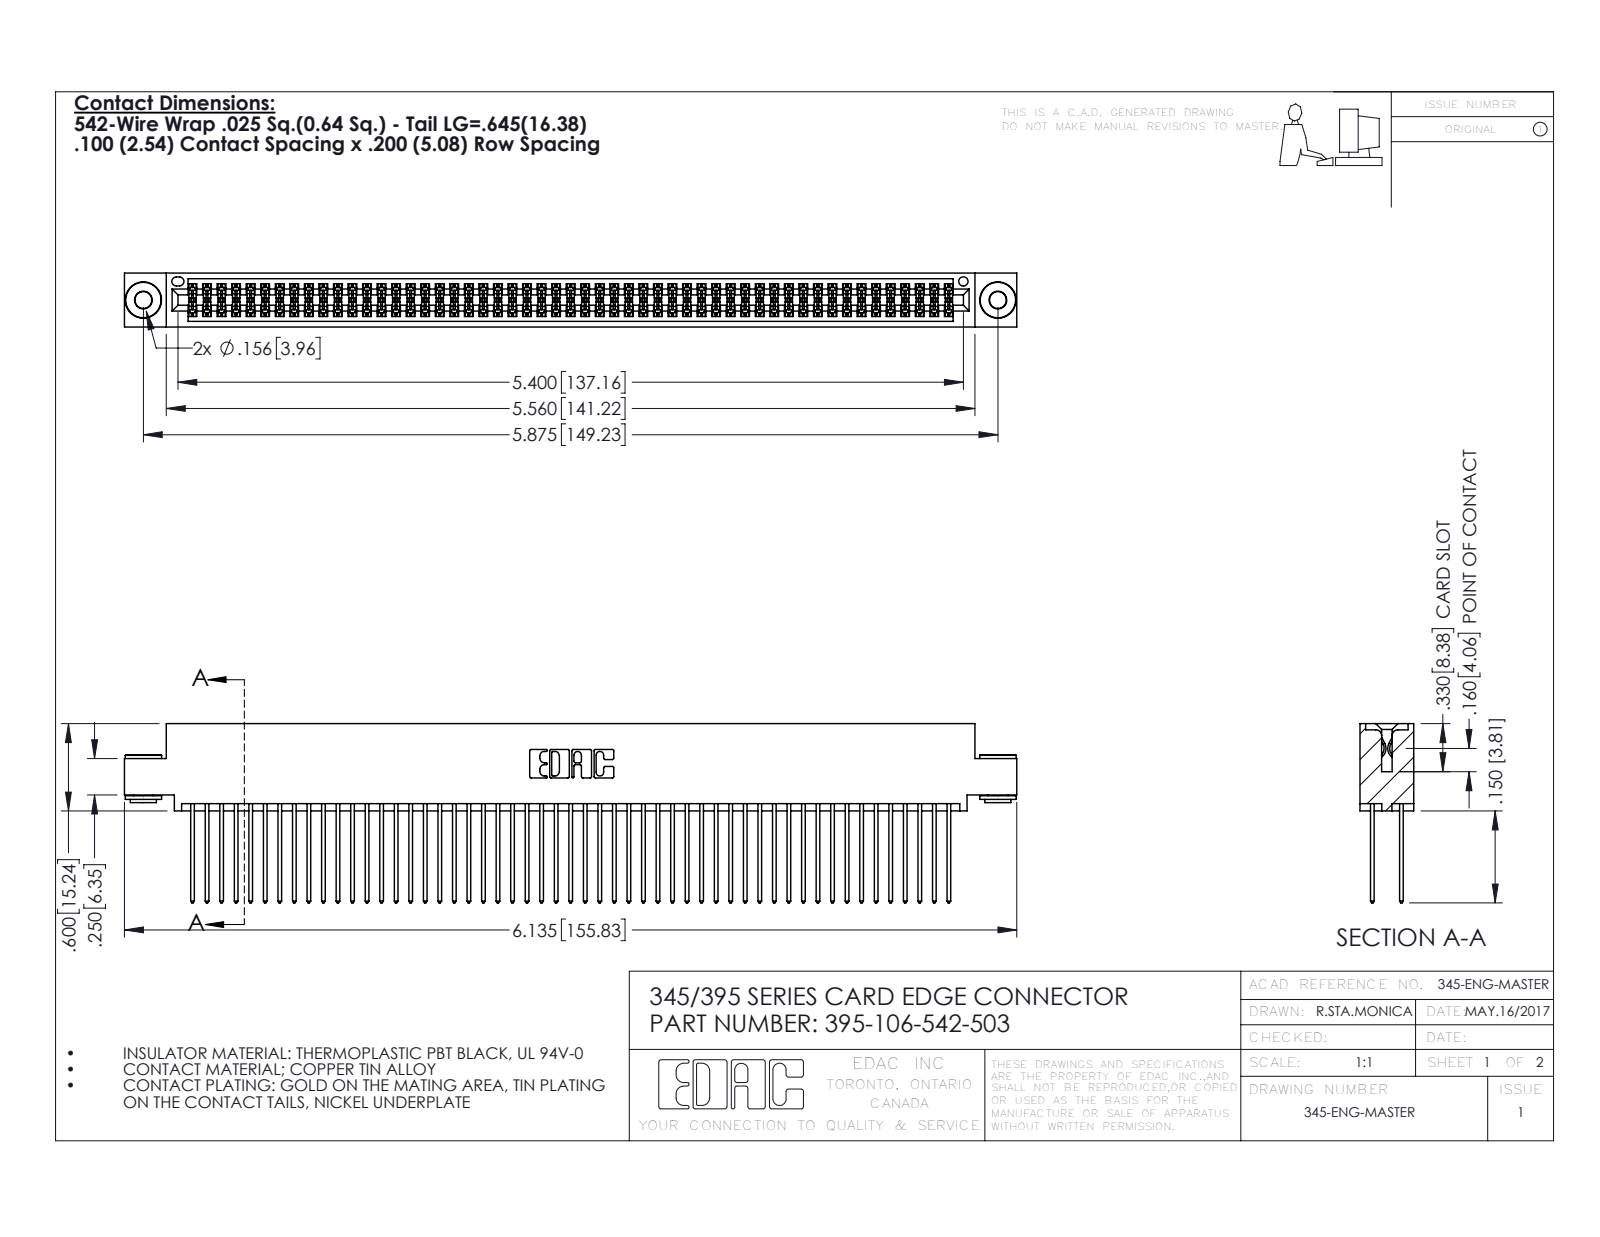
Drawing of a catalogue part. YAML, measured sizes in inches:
part_name: "345-292-001_345-293-142; 345-250-002_345-250-002-102; 395-106-542-503; 345 Part_0.110 Offset - 0.156 Dia-TH"
step_written_by: "SolidWorks 2016 (CONFIG_CONTROL_DESIGN)"
units: inches
bodies: {solids: 109, faces: 5468, planar: 3592, cylindrical: 1868, other: 8}
overall_size: [6.135, 1.232, 0.37]
volume: 0.957
surface_area: 40.3
round_holes:
  - {diameter: 0.116, count: 2}
  - {diameter: 0.156, count: 2}
  - {diameter: 0.064, count: 1}
round_bosses_or_shafts:
  - {diameter: 0.25, count: 2}
  - {diameter: 0.18, count: 2}
  - {diameter: 0.136, count: 2}
partial_cylinders:
  - {radius: 0.006, count: 159}
  - {radius: 0.01, count: 106}
  - {radius: 0.01, count: 22}
  - {radius: 0.007, count: 6}
  - {radius: 0.031, count: 6}
  - {radius: 0.026, count: 3}
  - {radius: 0.014, count: 2}
  - {radius: 0.019, count: 2}
face_to_face_distances: [0.072, 0.298, 0.2, 0.025, 0.098, 0.272, 0.225, 0.37, 0.175, 0.149]
hole_center_spacings: [0.27, 5.639, 5.875]
